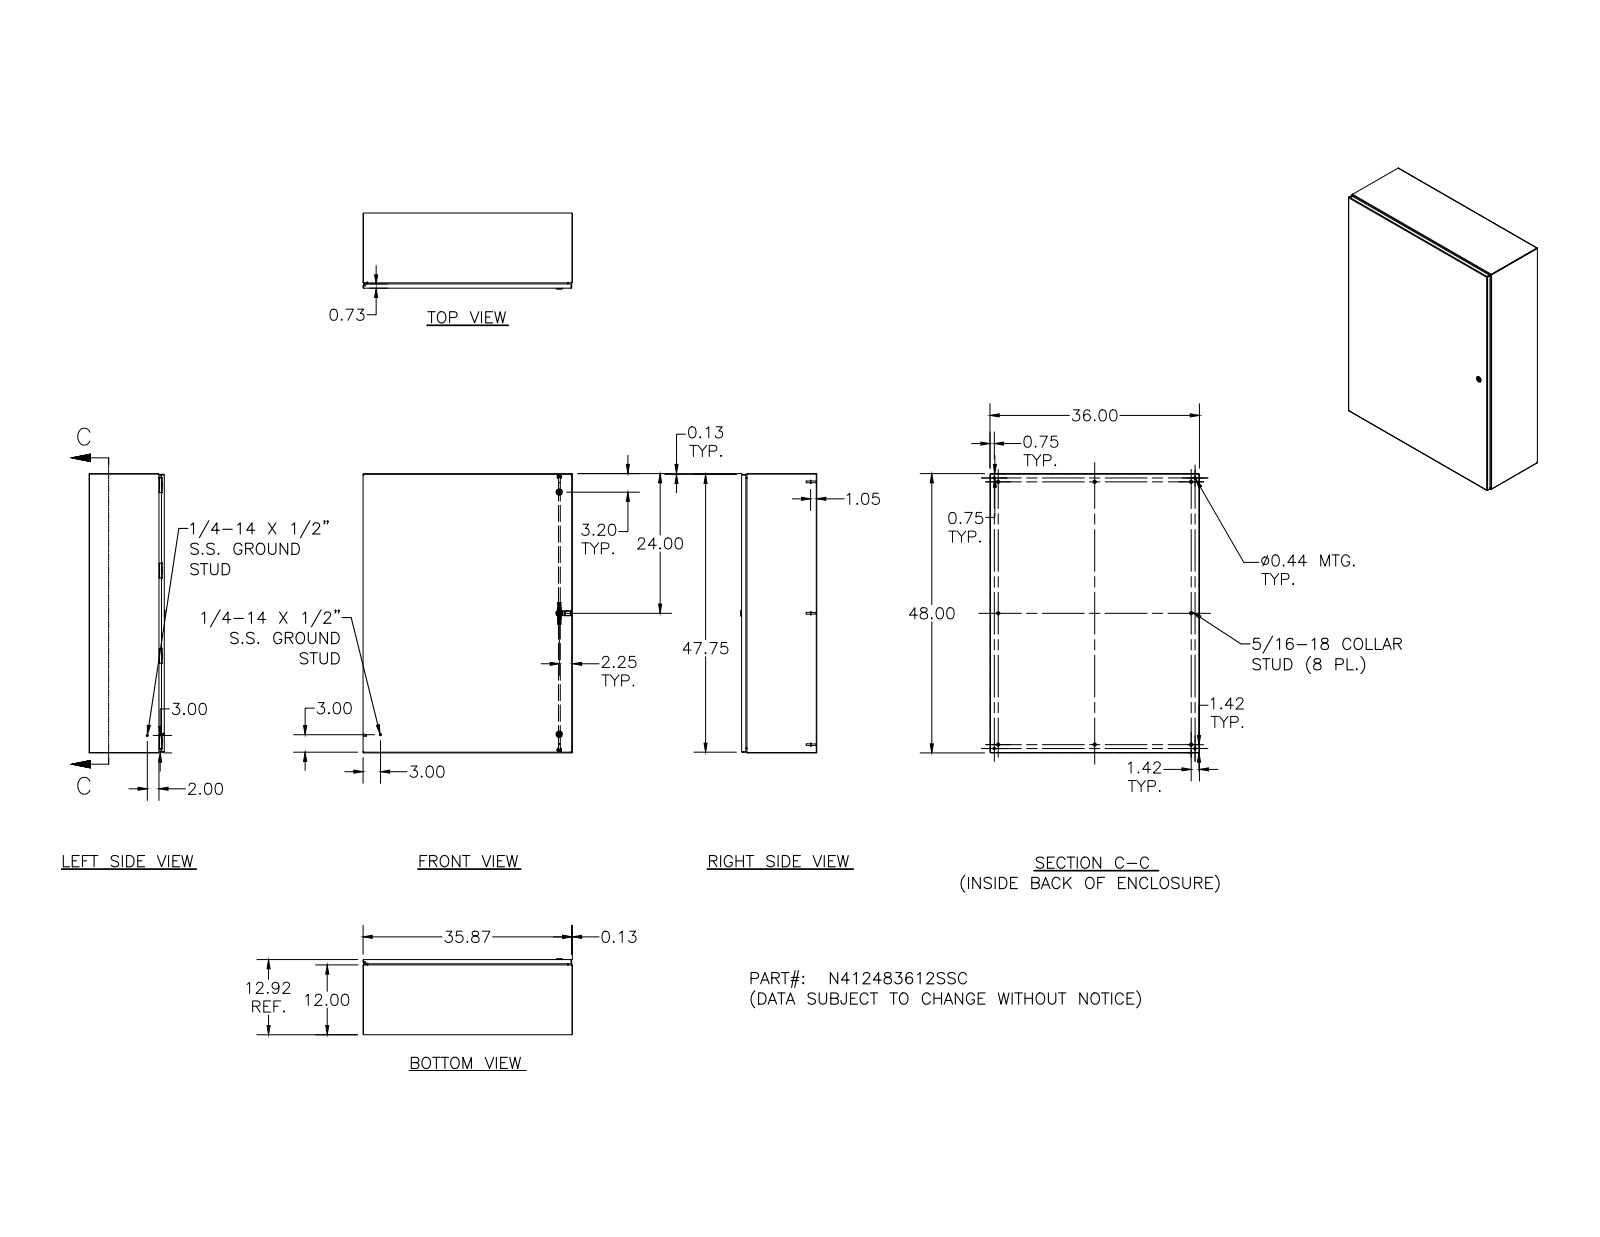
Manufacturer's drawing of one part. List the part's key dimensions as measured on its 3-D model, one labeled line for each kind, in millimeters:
Part name (STEP PRODUCT): N412483612SSC; N412483612SSCBTB; N4124812SSCLS; N4124812SSCRS (+8 more)
STEP written by: Autodesk Inventor 2011 (AUTOMOTIVE_DESIGN)
Units: millimetres
Bodies: 81 solids, 2655 faces (982 planar, 992 cylindrical, 681 other)
Overall size (bounding box): 1222.4 × 914.4 × 332.1
Volume: 7 130 000 mm³ · Surface area: 7 577 000 mm²
Round holes (diameter × count): ⌀2.4 ×8, ⌀3.9 ×8, ⌀4.2 ×8, ⌀4.4 ×8, ⌀4.7 ×8, ⌀5 ×5, ⌀4 ×4, ⌀4.2 ×4, ⌀11.1 ×4, ⌀2.7 ×2, ⌀4.1 ×2, ⌀4.3 ×2
Round bosses / shafts (diameter × count): ⌀6.4 ×18, ⌀14.3 ×8, ⌀9.1 ×8, ⌀8.1 ×8, ⌀7.6 ×8, ⌀7 ×8, ⌀6.5 ×8, ⌀4.2 ×8
Partial cylindrical surfaces — rounded edges, fillets, slot ends (radius × count): R1.3 ×50, R0.8 ×36, R0.4 ×34, R3.2 ×32, R0.3 ×30, R0.5 ×20, R2.7 ×18, R0.8 ×16
Main face-to-face distances: 1.9, 326.2, 324.3, 328.1, 912.5, 1217.3, 910.6, 914.4, 1215.4, 1219.2
Hole centre spacings: 372.5, 745.1, 372.5, 1117.6, 12.7, 16.7, 33.2, 372.7
